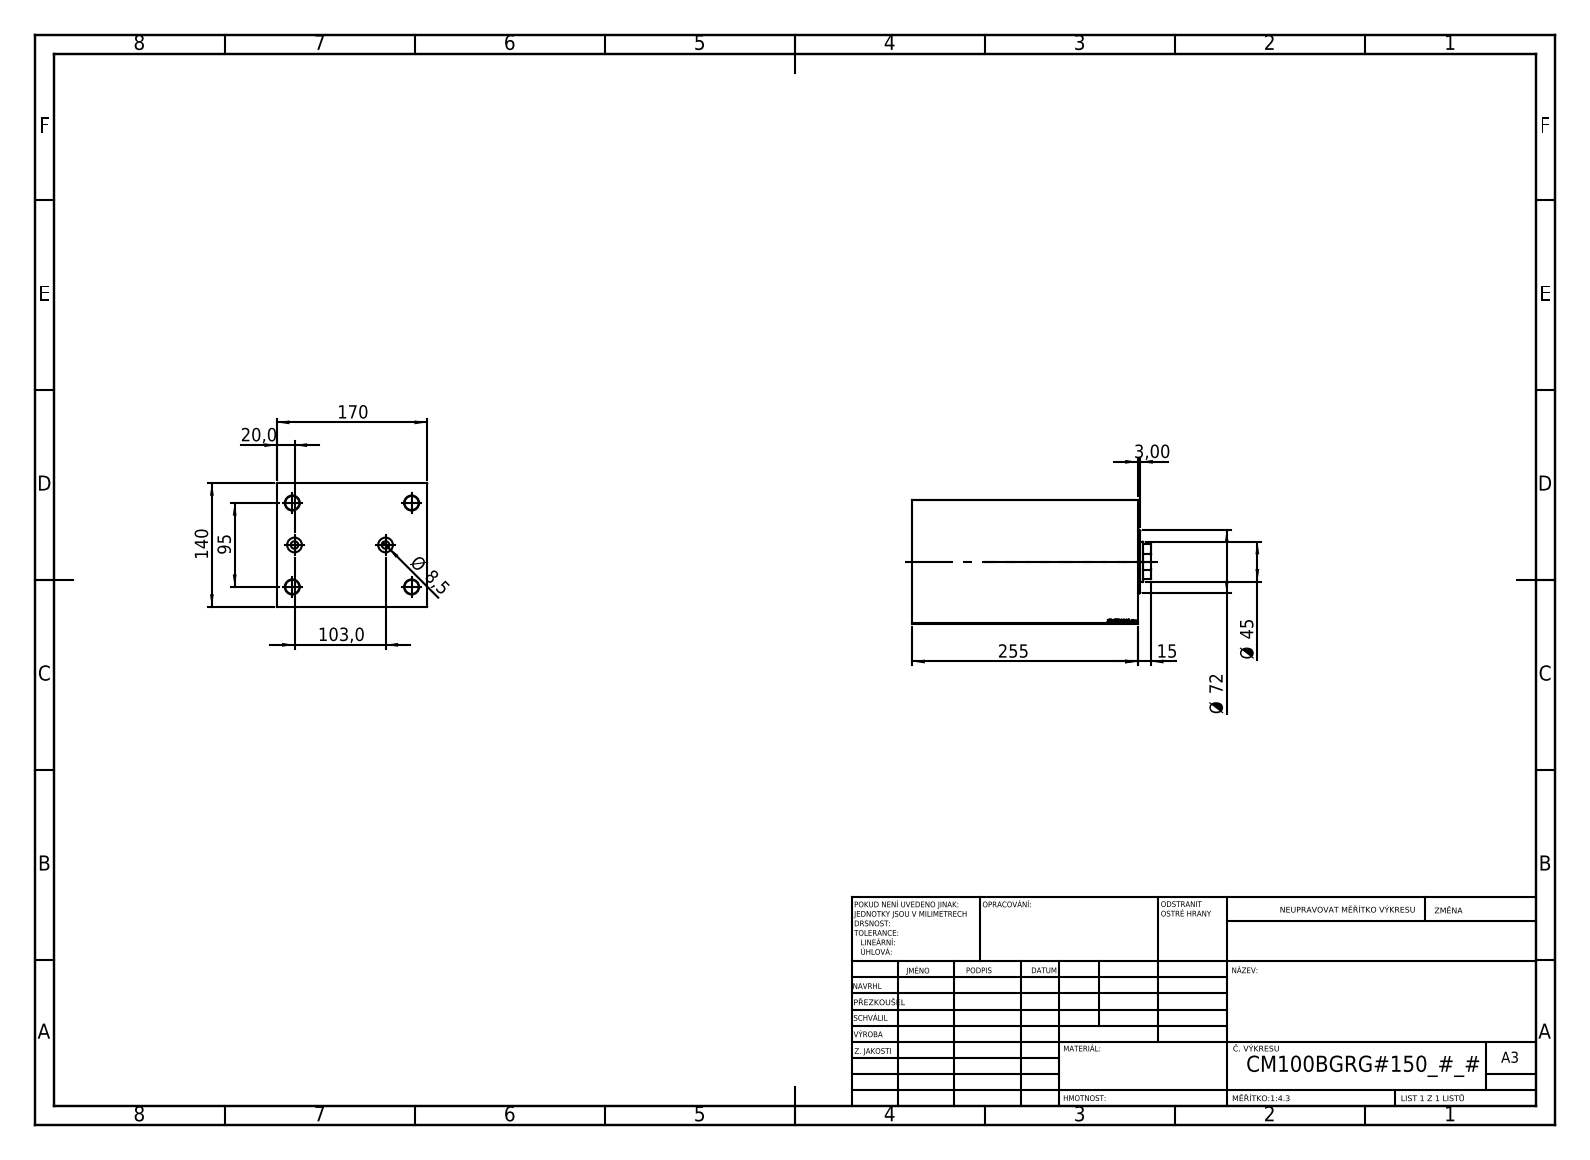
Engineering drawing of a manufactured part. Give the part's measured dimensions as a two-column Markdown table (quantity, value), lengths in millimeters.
| quantity | value |
| --- | --- |
| part name | V450CM_VC_B; V450CM_B_Body; V450CM_B_VCP |
| STEP written by | SolidWorks 2019 (CONFIG_CONTROL_DESIGN) |
| units | millimeters |
| bodies | 3 solids, 879 faces (401 planar, 52 cylindrical, 426 other) |
| overall size | 270 × 170 × 140 |
| volume | 5 057 000 mm³ |
| surface area | 384 559 mm² |
| round holes (diameter × count) | 16 × 4, 8.5 × 2, 16.66 × 2, 31.5 × 1, 45 × 1, 48.5 × 1, 49.5 × 1, 100 × 1, 102 × 1, 105 × 1 |
| round bosses / shafts (diameter × count) | 72 × 1 |
| partial cylindrical surfaces (radius × count) | 22 × 1 |
| main face-to-face distances | 140, 170, 255, 229, 26, 15, 240, 214, 90, 64 |
| hole center spacings | 82.54, 47.57, 55.92, 95, 115.7, 135, 140.76, 165.08 |
